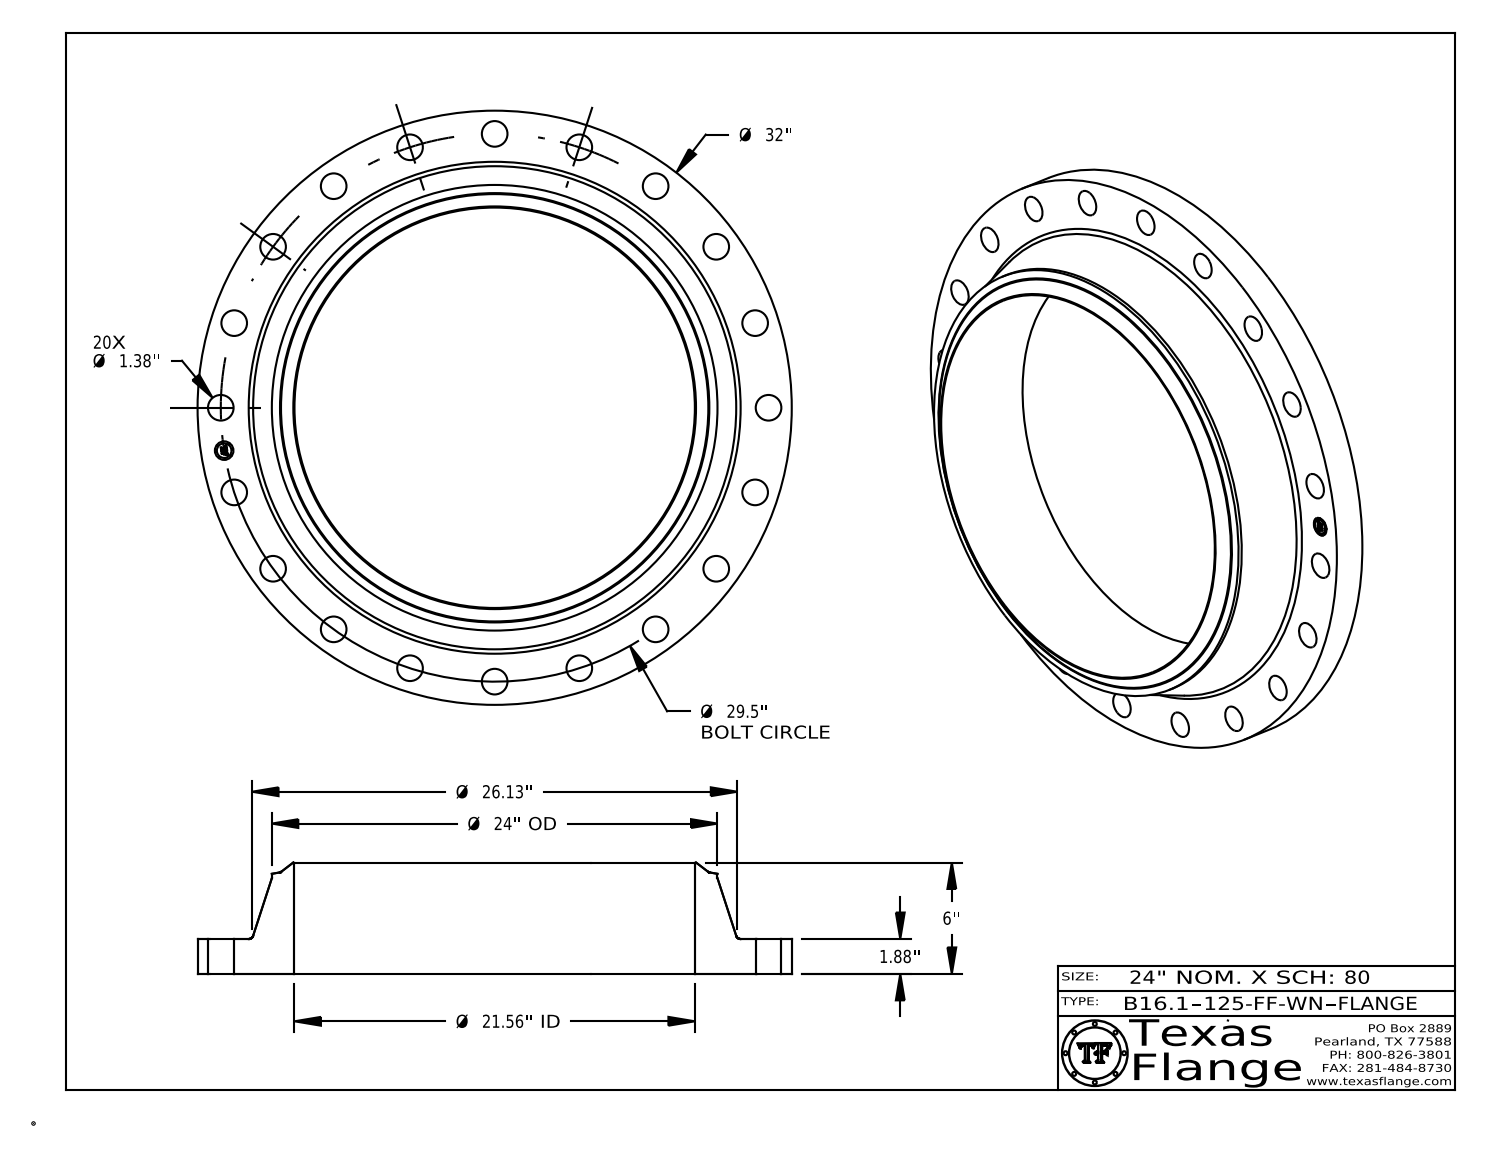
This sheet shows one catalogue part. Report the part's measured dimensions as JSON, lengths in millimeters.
{"part_name": "B16.1, Class 125-FF-WN", "step_written_by": "CATIA V5 STEP AP214 (AUTOMOTIVE_DESIGN)", "units": "millimeters", "bodies": {"solids": 1, "faces": 444, "planar": 368, "cylindrical": 66, "other": 10}, "overall_size": [812.8, 812.8, 152.4], "volume_mm3": 20190000, "surface_area_mm2": 1155000, "round_holes": [[35.1, 20], [25.4, 1], [547.7, 1]], "round_bosses_or_shafts": [[1.5, 8], [812.8, 1], [609.6, 1], [20, 1]], "face_to_face_distances": [47.8, 152.4, 104.6, 47.4, 0.4, 105, 7.6, 7.4, 1.4, 4.9], "hole_center_spacings": [374.7, 740.1, 117.2, 440.4, 529.8, 606.2, 667.6, 231.5]}
